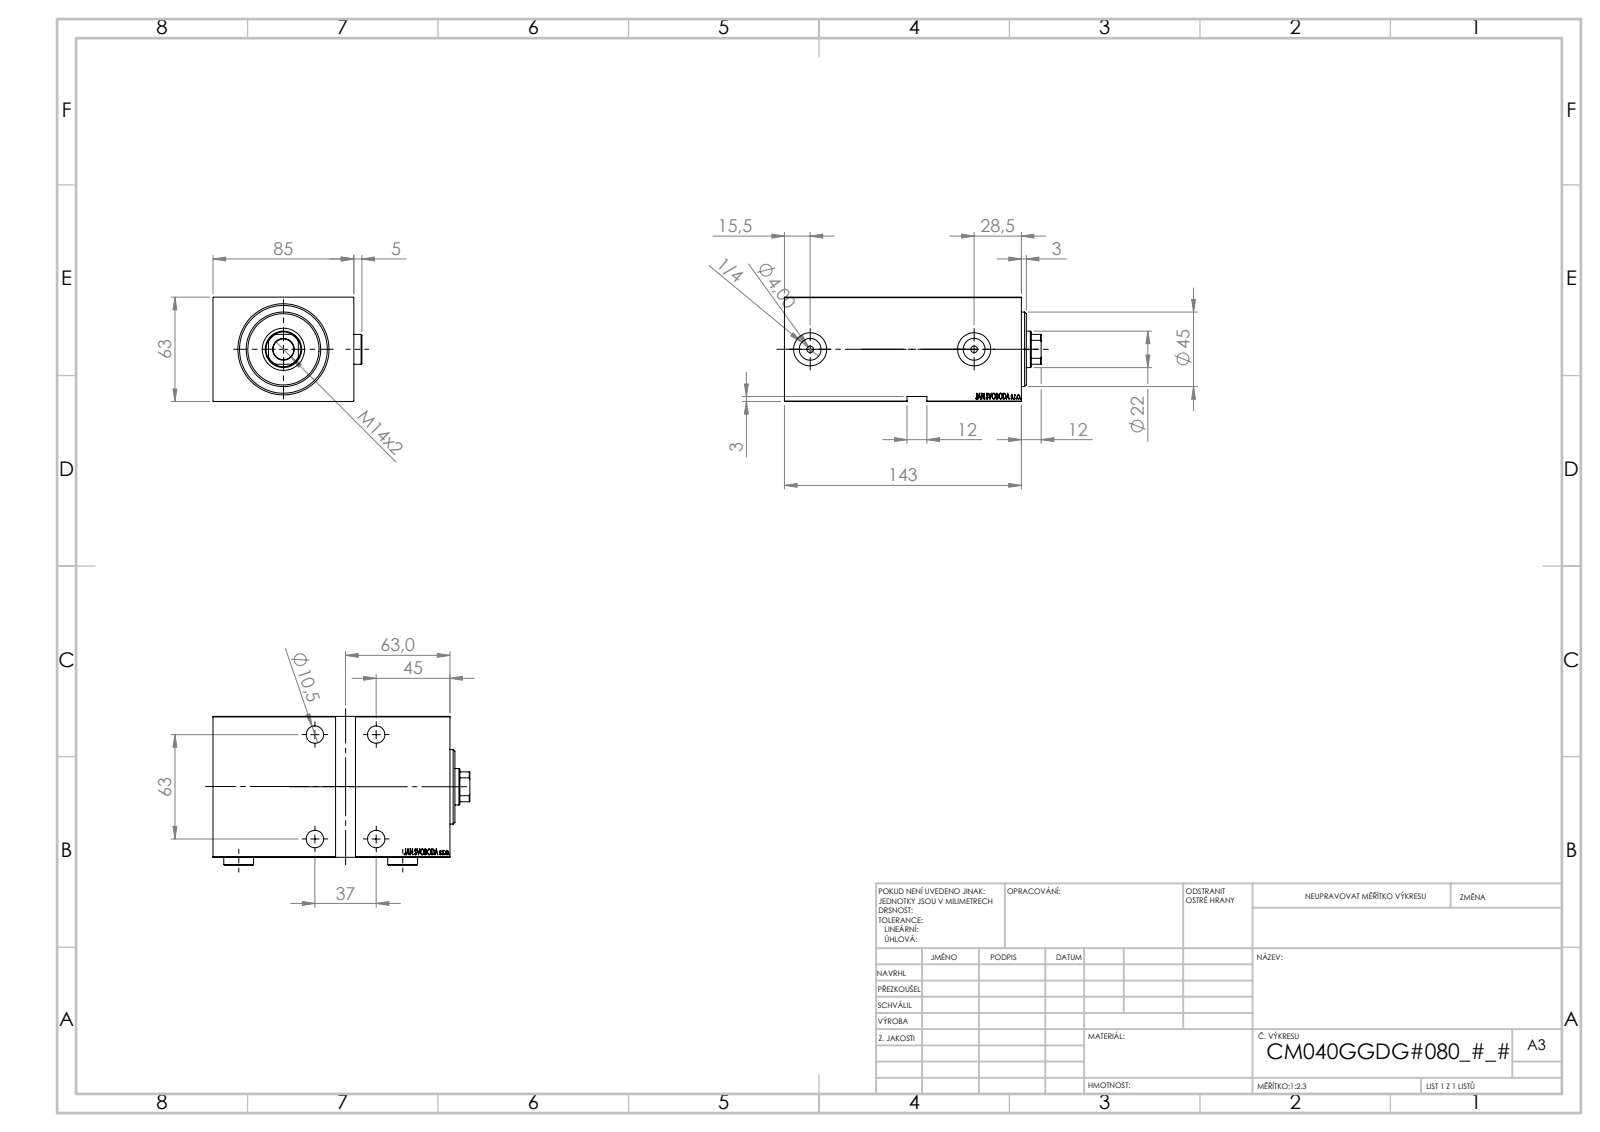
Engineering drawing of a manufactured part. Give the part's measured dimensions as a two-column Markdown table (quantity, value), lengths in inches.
| quantity | value |
| --- | --- |
| part name | Zatka_OIL_PORT; V450CM_G_Body; V450CM_VC_G; V450CM_G_VCP |
| STEP written by | SolidWorks 2019 (CONFIG_CONTROL_DESIGN) |
| units | inches |
| bodies | 5 solids, 915 faces (447 planar, 70 cylindrical, 398 other) |
| overall size | 6.102 × 3.539 × 2.48 |
| volume | 40.04 in³ |
| surface area | 162.8 in² |
| round holes (diameter × count) | 0.413 × 4, 0.65 × 4, 0.157 × 2, 0.518 × 2, 0.787 × 2, 0.492 × 1, 0.866 × 1, 1.004 × 1, 1.575 × 1, 1.654 × 1, 2.087 × 1 |
| round bosses / shafts (diameter × count) | 0.709 × 2, 1.772 × 1, 1.063 × 1 |
| partial cylindrical surfaces (radius × count) | 0.413 × 1 |
| main face-to-face distances | 2.48, 3.346, 5.63, 0.472, 5.157, 0.197, 5.433, 4.961, 0.118, 2.362 |
| hole center spacings | 1.457, 2.48, 2.876, 3.898 |
